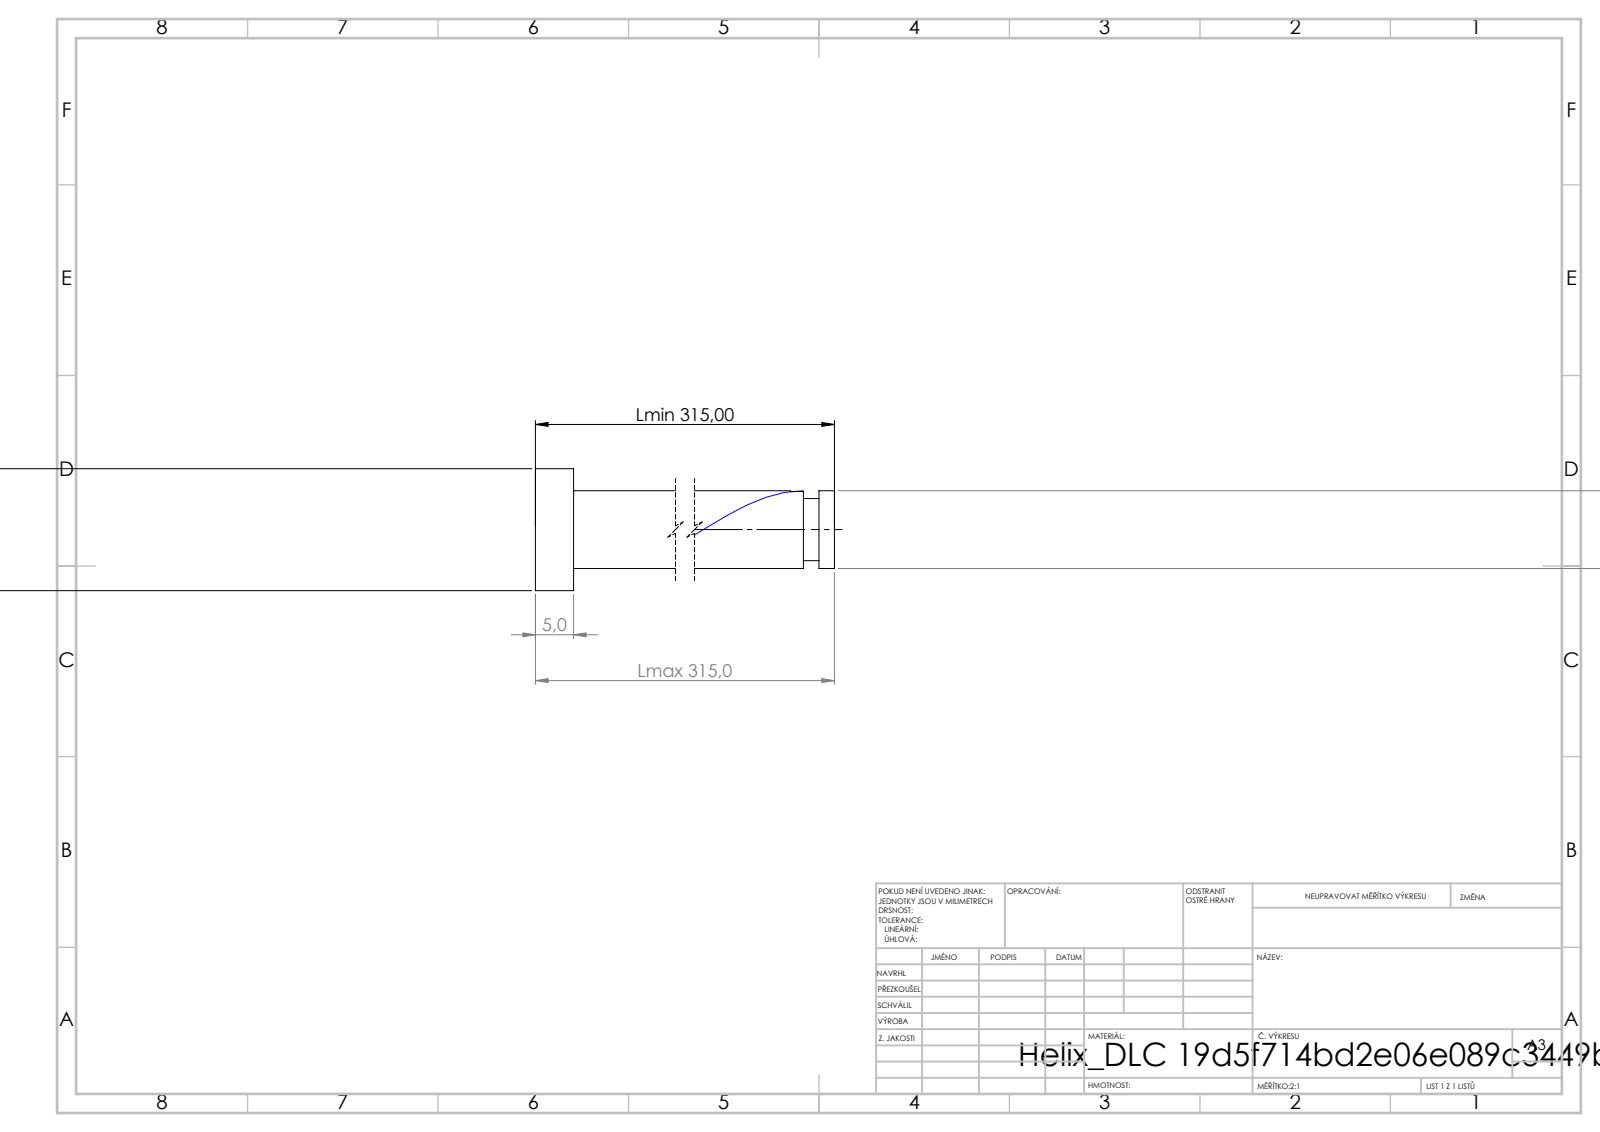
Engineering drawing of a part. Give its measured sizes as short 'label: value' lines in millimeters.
written by: SolidWorks 2019 (CONFIG_CONTROL_DESIGN)
unit: mm
bodies: 1 solid, 21 faces (6 planar, 14 cylindrical, 1 other)
size: 315 × 16 × 16
volume: 26 030 mm³; area: 10 822 mm²
bosses: 1× ⌀16, 1× ⌀10.2, 1× ⌀8.16
face distances: 5, 315, 310, 2.04, 312.96, 307.96, 310.92, 305.92, 4.08, 153.42
